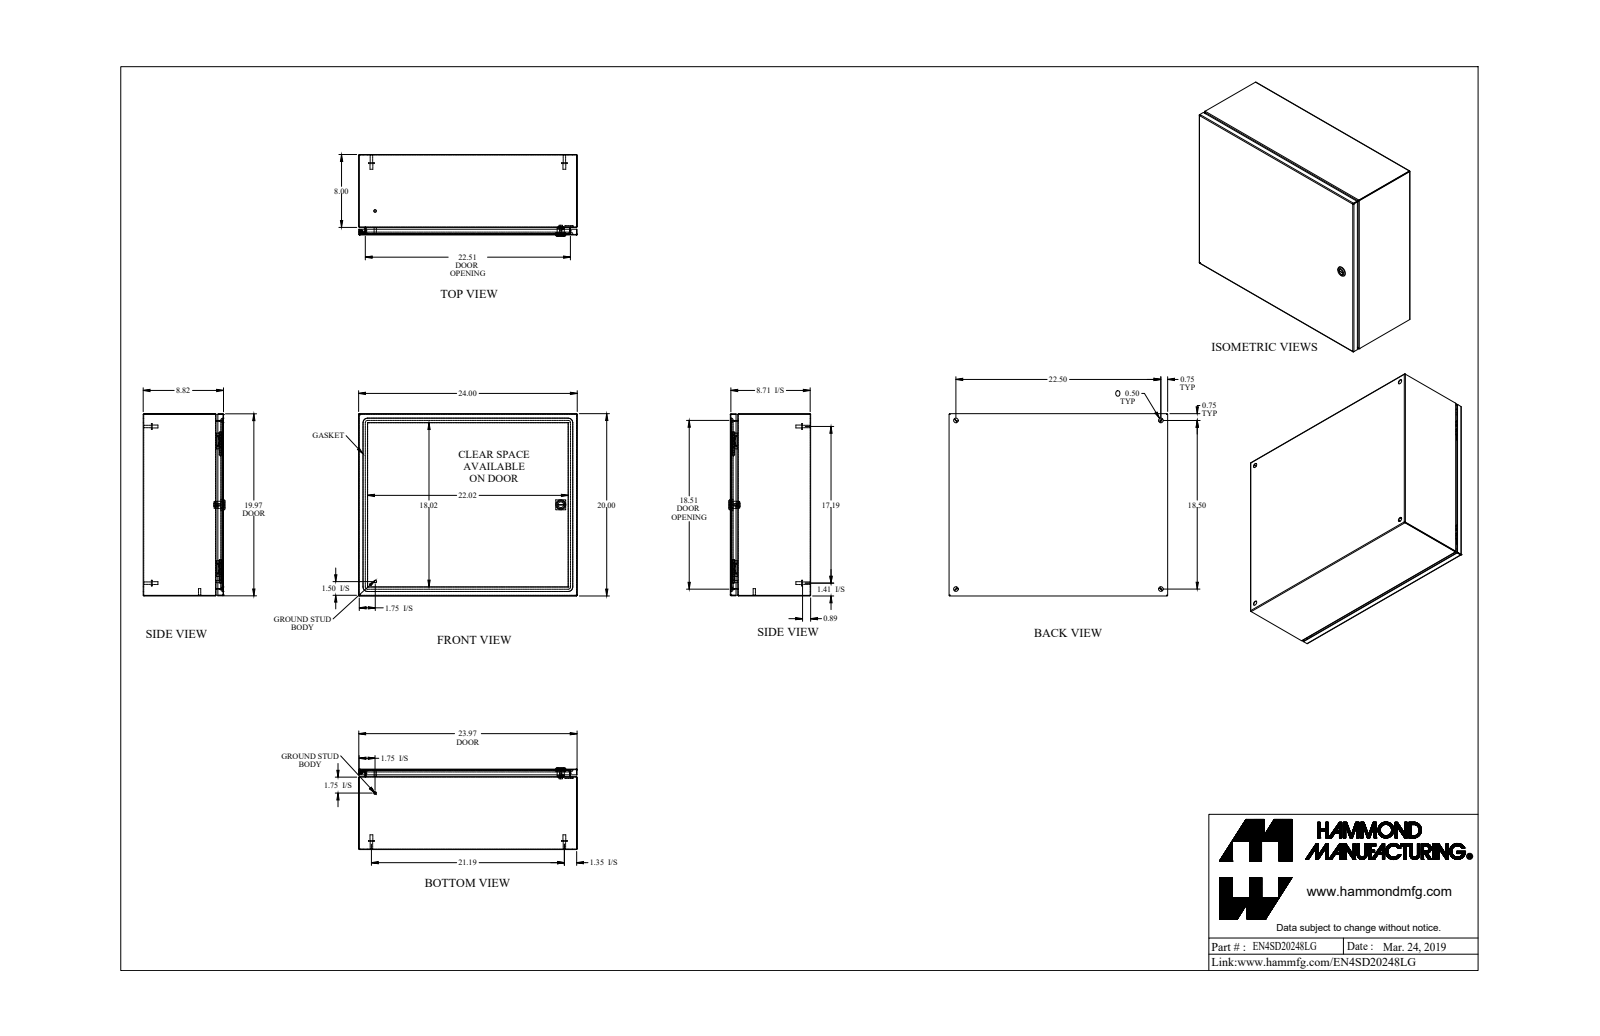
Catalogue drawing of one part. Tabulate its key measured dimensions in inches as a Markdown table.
| quantity | value |
| --- | --- |
| part name | EN4SD20248LG_Default |
| STEP written by | SolidWorks 2019 (CONFIG_CONTROL_DESIGN) |
| units | inches |
| bodies | 21 solids, 634 faces (285 planar, 213 cylindrical, 136 other) |
| overall size | 24 × 20 × 8.982 |
| volume | 113.2 in³ |
| surface area | 3 865 in² |
| round holes (diameter × count) | 0.5 × 4, 0.172 × 1, 0.232 × 1, 0.24 × 1, 0.242 × 1, 0.625 × 1, 0.785 × 1 |
| round bosses / shafts (diameter × count) | 0.625 × 4, 0.313 × 4, 0.27 × 4, 0.281 × 2, 0.25 × 2, 1.1 × 1, 0.525 × 1, 0.455 × 1 |
| partial cylindrical surfaces (radius × count) | 0.029 × 21, 0.086 × 21, 0.25 × 16, 19 × 8, 0.006 × 4, 0.062 × 4, 0.499 × 4, 0.125 × 2 |
| main face-to-face distances | 0.057, 8.765, 8.708, 8.822, 19.943, 23.943, 19.886, 20, 23.886, 24 |
| hole center spacings | 18.5, 22.5, 23.351, 29.129, 9.31, 9.311 |
